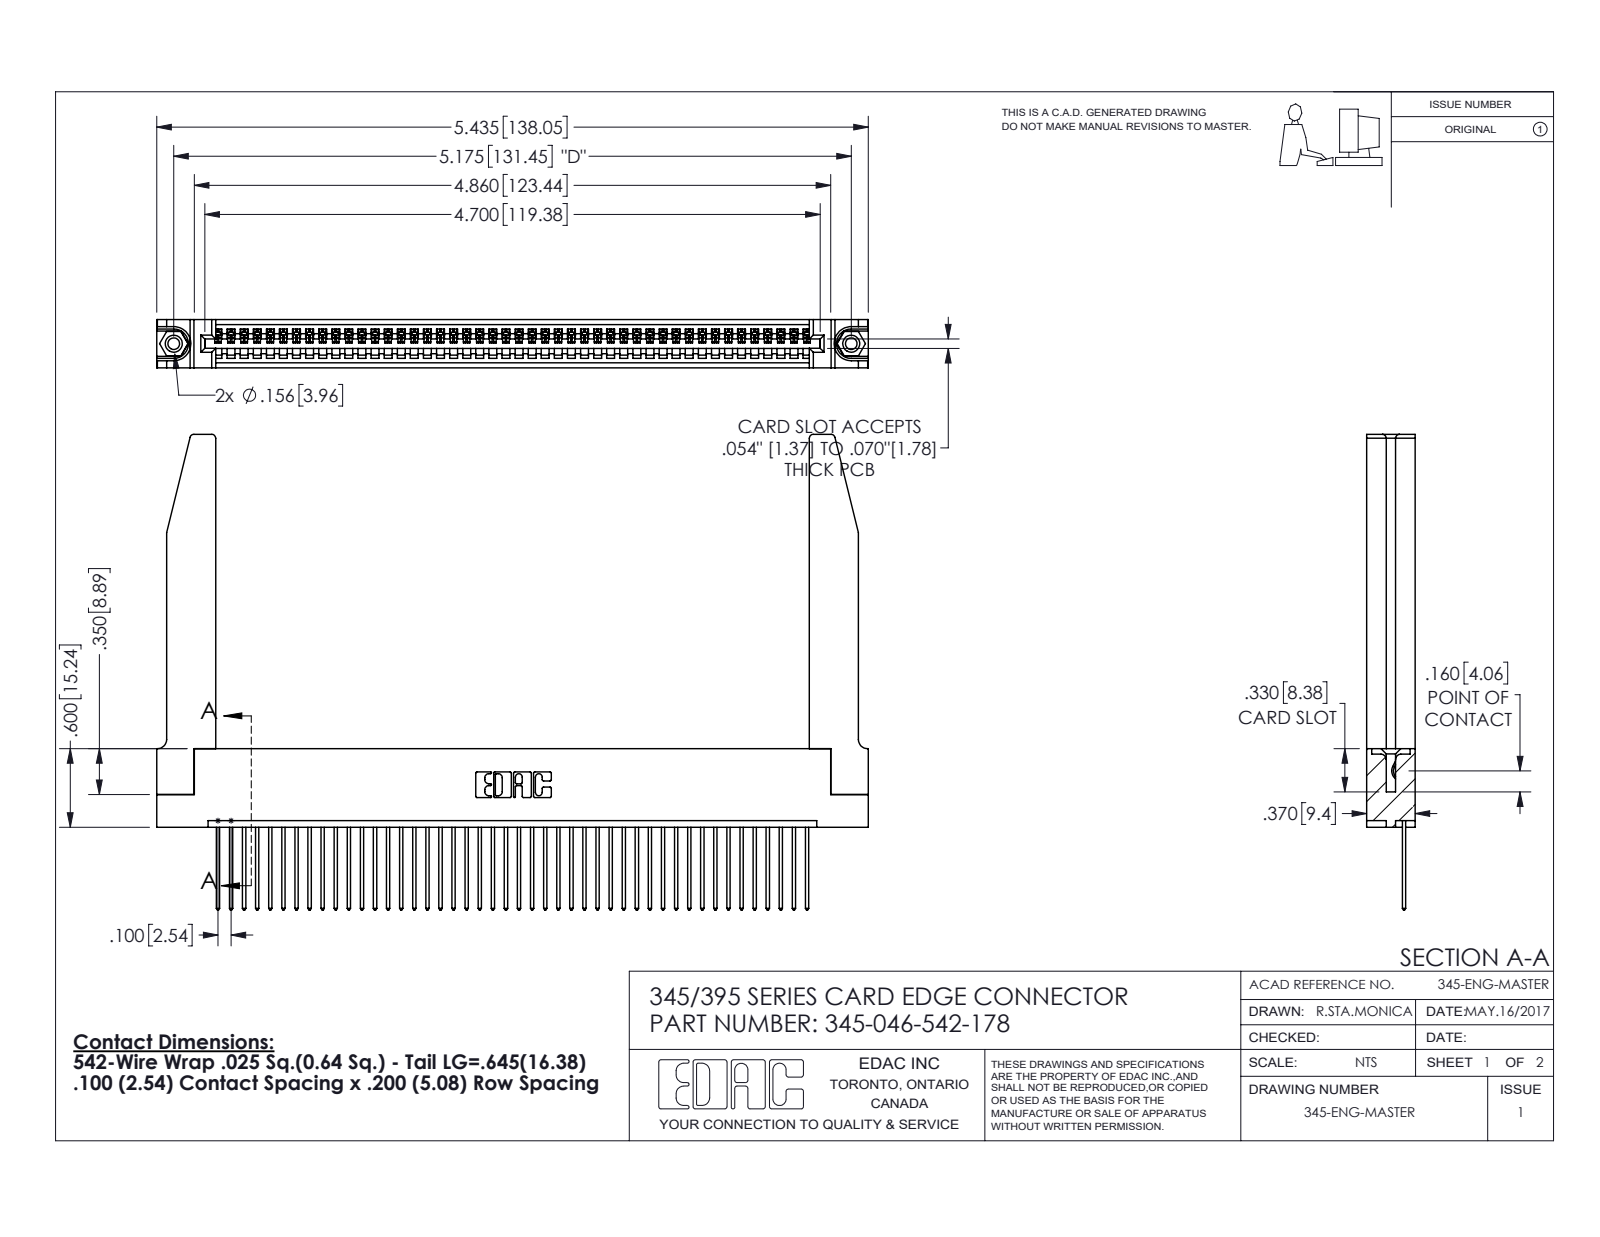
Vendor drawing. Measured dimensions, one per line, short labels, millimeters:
name: 345-292-001_345-293-142; 345-250-001_345-250-001-102; 345-220-078_345-220-078; 345-046-542-178 (+1 more)
written by: SolidWorks 2016 (CONFIG_CONTROL_DESIGN)
unit: mm
bodies: 51 solids, 3028 faces (2062 planar, 914 cylindrical, 52 other)
size: 138.1 × 92.3 × 9.4
volume: 21 020 mm³; area: 25 150 mm²
holes: 2× ⌀2.3, 2× ⌀3.2, 2× ⌀4, 1× ⌀1.6
bosses: 2× ⌀3.9
rounds: 92× R0.2, 92× R0.3, 22× R0.3, 8× R0.8, 6× R0.2, 6× R0.8, 3× R0.7, 2× R0.8
face distances: 1.8, 9.4, 7.6, 2.5, 6.9, 0.6, 5.1, 5.7, 3.8, 3.8
hole spacings: 6.9, 125.5, 131.4
